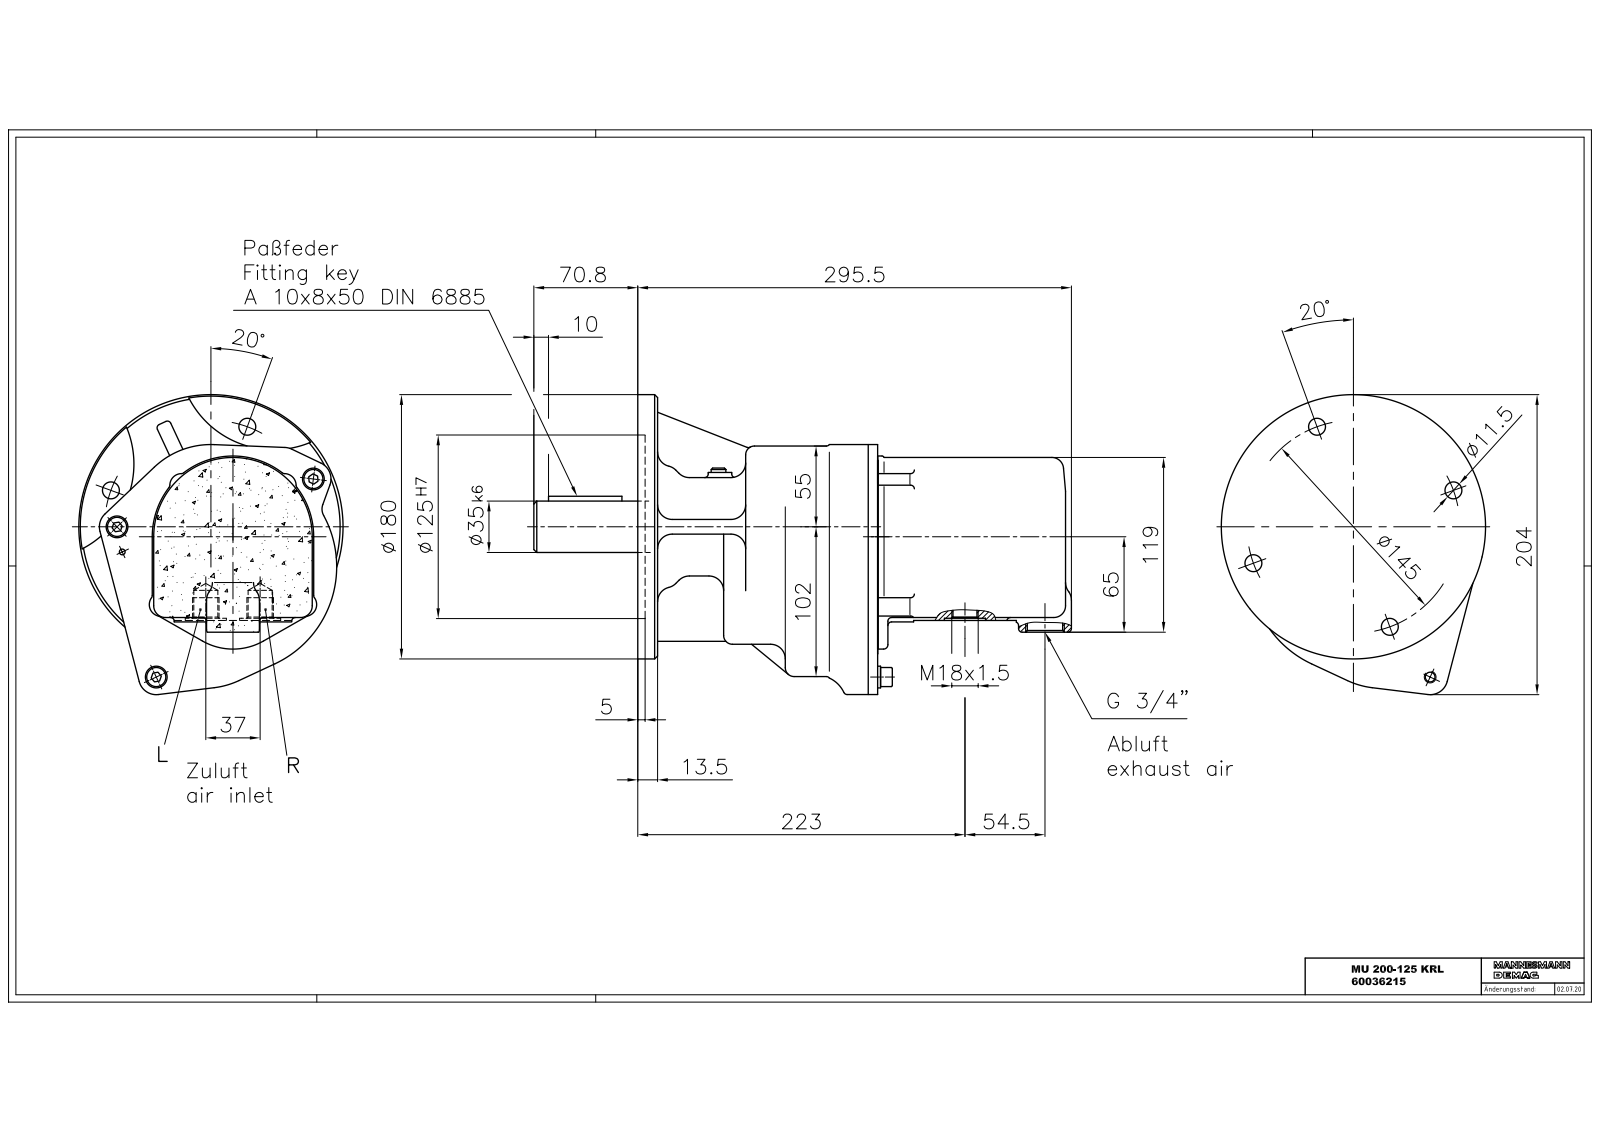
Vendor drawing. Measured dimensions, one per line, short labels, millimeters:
name: MU 200-125 KRL_60036215
written by: Autodesk Inventor 2021 (AUTOMOTIVE_DESIGN)
unit: mm
bodies: 1 solid, 1274 faces (479 planar, 456 cylindrical, 339 other)
size: 366.7 × 204.41 × 180
volume: 3 756 000 mm³; area: 268 171 mm²
holes: 16× ⌀2.08, 4× ⌀4.92, 4× ⌀9.5, 4× ⌀11.5, 2× ⌀6.5, 2× ⌀8.5, 2× ⌀16.38, 2× ⌀28, 1× ⌀2.5, 1× ⌀2.8, 1× ⌀4, 1× ⌀4.2
bosses: 16× ⌀2.1, 3× ⌀13, 3× ⌀8, 2× ⌀14.8, 1× ⌀180, 1× ⌀35, 1× ⌀16, 1× ⌀10
rounds: 57× R2, 40× R2.5, 14× R8, 12× R10, 9× R1.5, 8× R3, 8× R4, 8× R11
face distances: 1, 5, 7.5, 163.9, 158.9, 46.8, 112.1, 117.1, 8.5, 150.4
hole spacings: 7.05, 2.75, 7.83, 13.83, 7.06, 9.97, 5.39, 7.04
